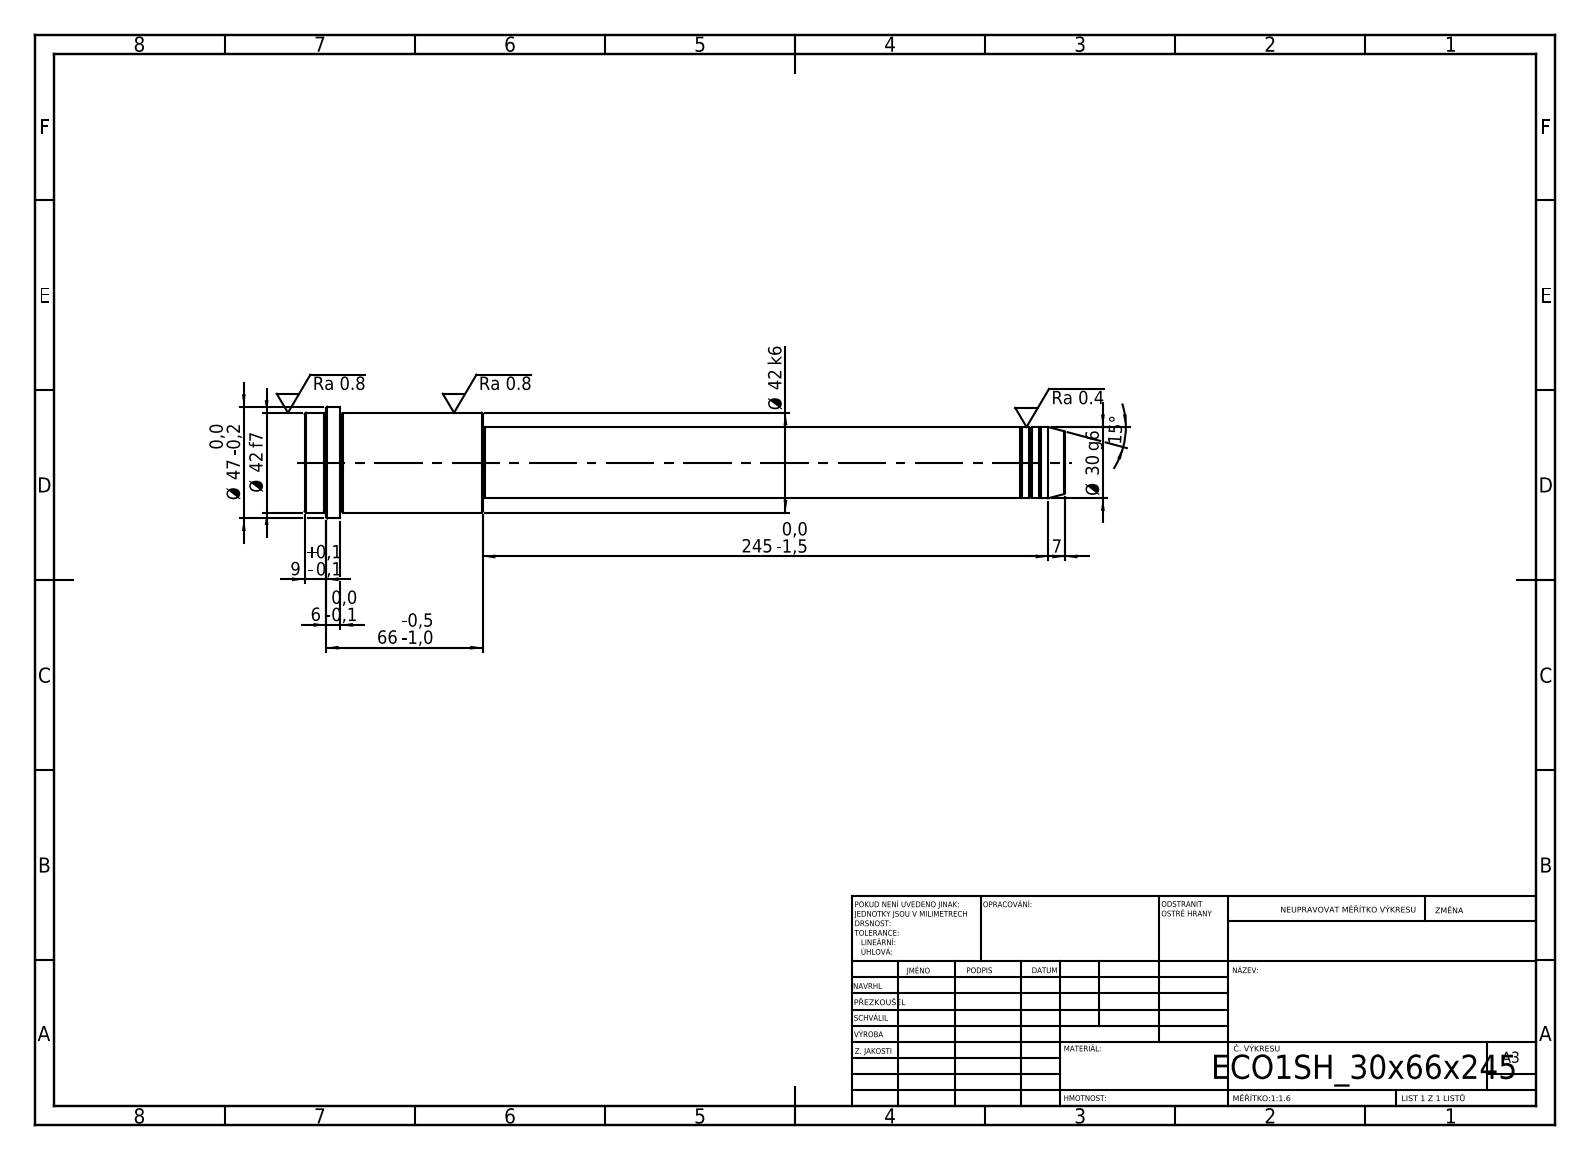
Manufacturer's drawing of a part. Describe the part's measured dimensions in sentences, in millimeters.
Its 3-D file was written by "SolidWorks 2019 (CONFIG_CONTROL_DESIGN)". It is 1 solid with 52 faces: 6 planar, 16 cylindrical and 30 other. Overall it measures 320 by 47 by 47 millimeters. Its volume is 278 281 cubic millimeters and its surface area 36 621 square millimeters. Round bosses or shafts: 1 of diameter 47, 1 of diameter 42, 1 of diameter 30, 1 of diameter 29. The main face-to-face distances are 75, 245, 320, 305, 60, 15, 311, 66, 6, 9.
